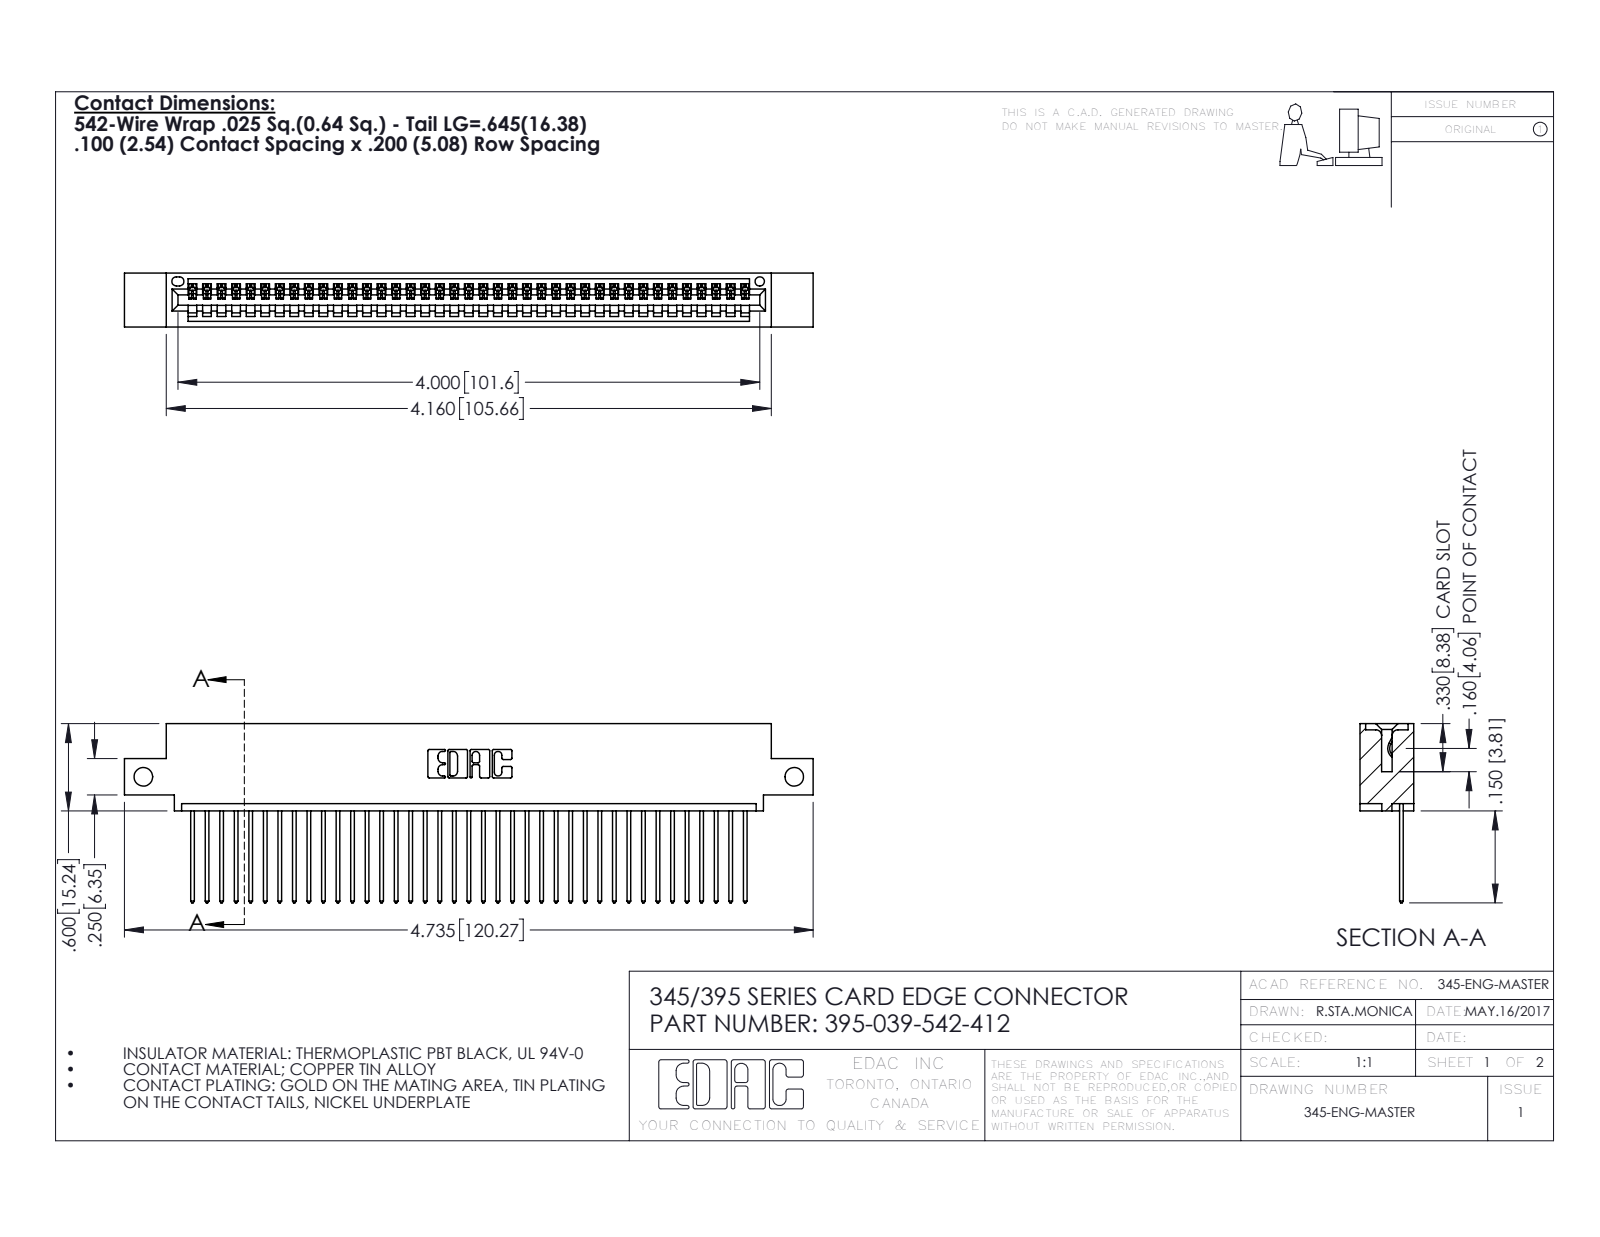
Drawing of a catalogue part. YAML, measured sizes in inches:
part_name: "395-039-542-412; 345-292-001_345-293-142; 345 Part_0.110 Offset - Side Mount"
step_written_by: "SolidWorks 2016 (CONFIG_CONTROL_DESIGN)"
units: inches
bodies: {solids: 40, faces: 2392, planar: 1644, cylindrical: 748, other: 0}
overall_size: [4.735, 1.232, 0.37]
volume: 0.691
surface_area: 24.02
round_holes:
  - {diameter: 0.128, count: 2}
  - {diameter: 0.064, count: 1}
partial_cylinders:
  - {radius: 0.006, count: 78}
  - {radius: 0.01, count: 78}
  - {radius: 0.01, count: 22}
  - {radius: 0.007, count: 6}
  - {radius: 0.031, count: 6}
  - {radius: 0.026, count: 3}
  - {radius: 0.031, count: 2}
  - {radius: 0.04, count: 2}
face_to_face_distances: [0.072, 0.298, 0.37, 0.098, 0.272, 0.025, 0.2, 0.225, 0.149, 0.072]
hole_center_spacings: [4.475]
